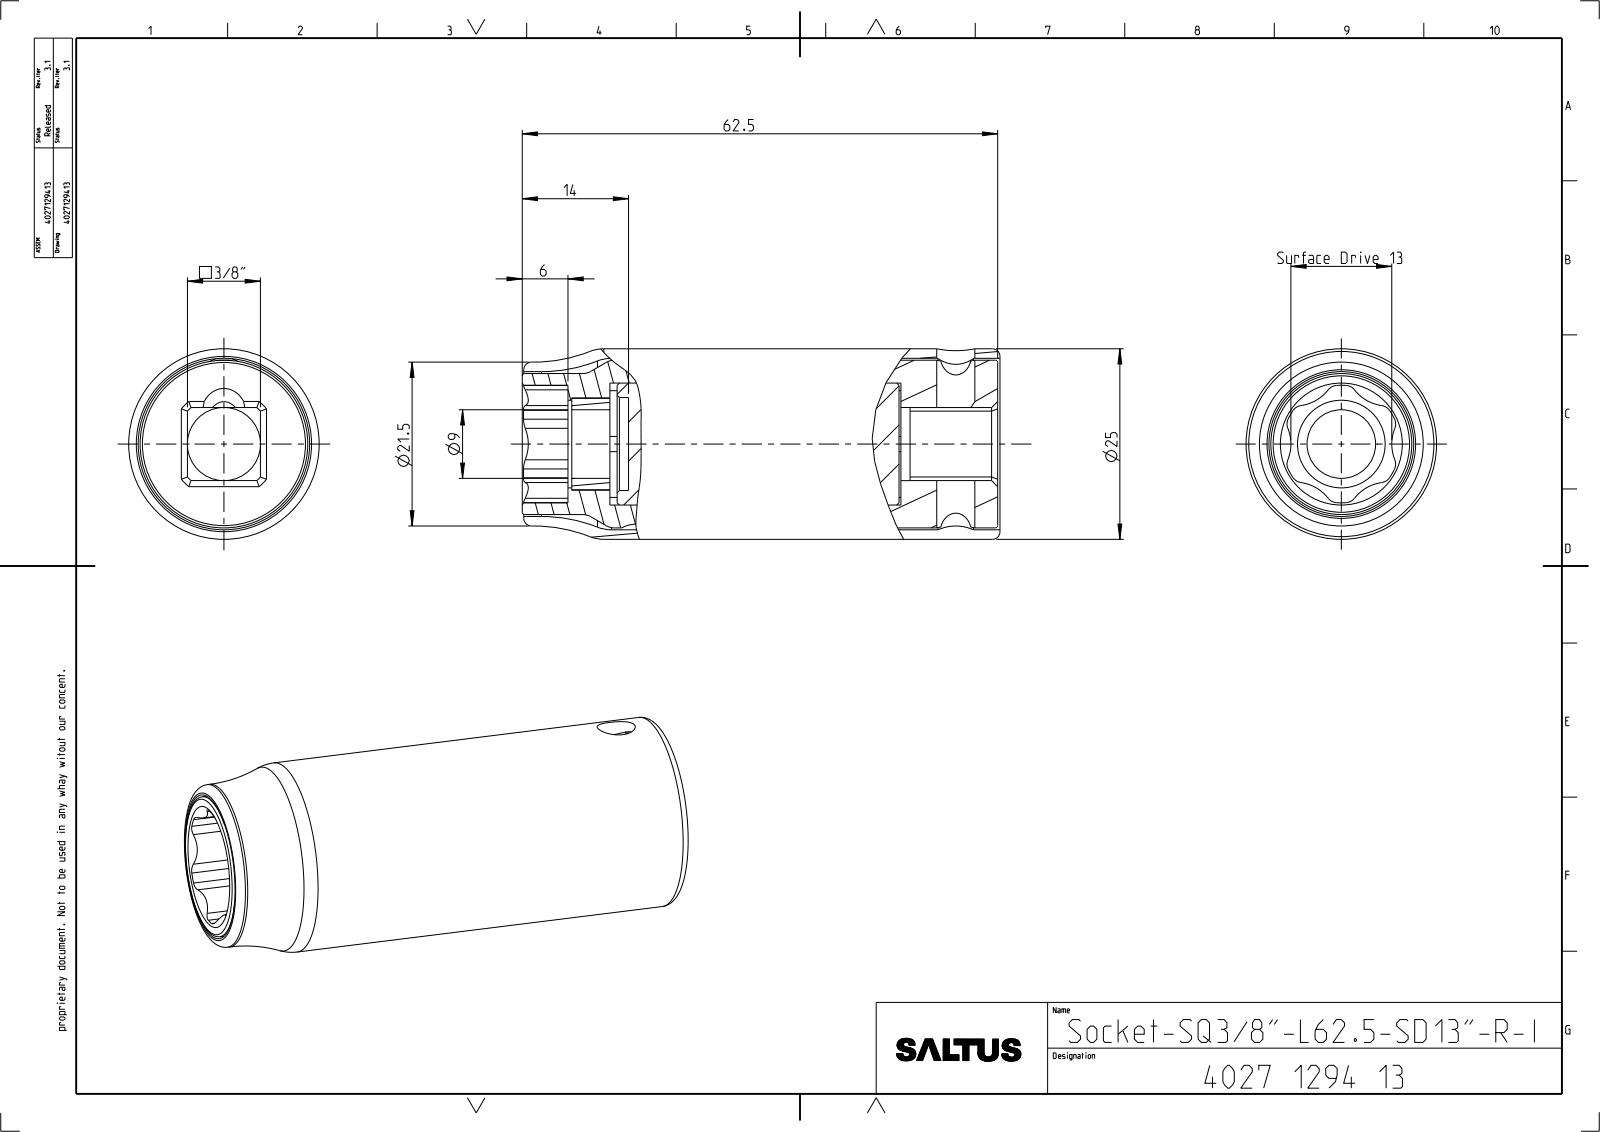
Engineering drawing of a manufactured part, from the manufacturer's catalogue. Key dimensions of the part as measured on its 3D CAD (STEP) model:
Part name (STEP PRODUCT): 4027031422_AF2; 4027031423_AF2; 4027030897_AF0; 4027907736_AF1 (+4 more)
STEP written by: CREO PARAMETRIC BY PTC INC, 2022414 (CONFIG_CONTROL_DESIGN)
Units: millimetres
Bodies: 9 solids, 279 faces (63 planar, 142 cylindrical, 74 other)
Overall size (bounding box): 62.7 × 25 × 25
Volume: 12 741 mm³ · Surface area: 26 005 mm²
Round holes (diameter × count): ⌀2 ×2, ⌀5 ×1, ⌀9 ×1, ⌀9.6 ×1, ⌀11.5 ×1, ⌀12.1 ×1, ⌀19 ×1, ⌀20.53 ×1, ⌀22.5 ×1
Round bosses / shafts (diameter × count): ⌀25 ×1, ⌀22 ×1, ⌀21.5 ×1, ⌀18.5 ×1, ⌀12 ×1
Partial cylindrical surfaces — rounded edges, fillets, slot ends (radius × count): R1.5 ×12, R2 ×6, R5.5 ×6, R3 ×1, R6.45 ×1, R7.71 ×1
Main face-to-face distances: 50.9, 9.58, 12.7, 38.2, 11.5, 49.5, 56.4, 43.7, 5.5, 12.9
Hole centre spacings: 13.25, 25.4, 38.65
